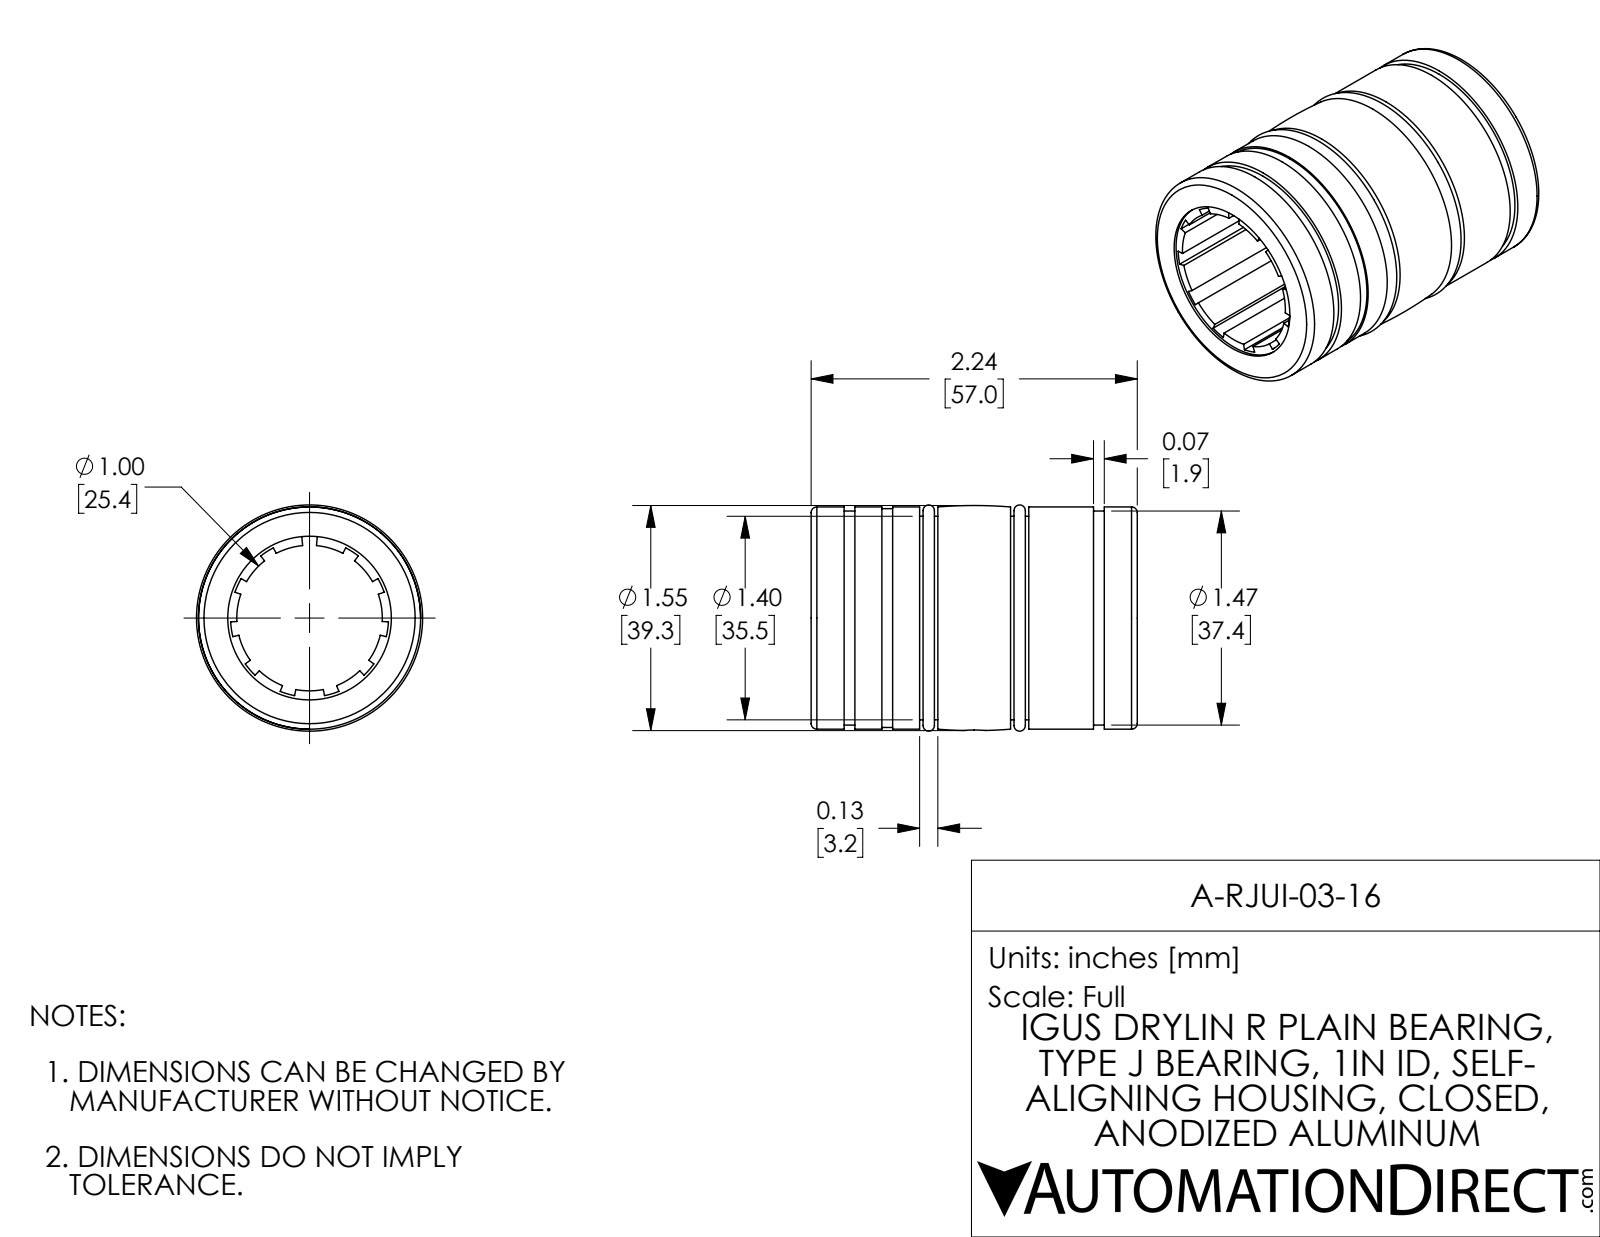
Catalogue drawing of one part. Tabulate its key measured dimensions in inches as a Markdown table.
| quantity | value |
| --- | --- |
| part name | A-RJUI-03-16 |
| STEP written by | SolidWorks 2017 (AUTOMOTIVE_DESIGN) |
| units | inches |
| bodies | 4 solids, 161 faces (81 planar, 66 cylindrical, 14 other) |
| overall size | 2.242 × 1.555 × 1.555 |
| volume | 2.178 in³ |
| surface area | 41.82 in² |
| round holes (diameter × count) | 0.156 × 1, 1.125 × 1, 1.203 × 1 |
| round bosses / shafts (diameter × count) | 1.527 × 1, 1.504 × 1, 1.471 × 1, 1.399 × 1, 1.125 × 1, 0.15 × 1 |
| partial cylindrical surfaces (radius × count) | 0.5 × 1, 0.543 × 1, 0.594 × 1 |
| main face-to-face distances | 2.242, 0.746, 1.496, 0.871, 1.371, 0.125, 0.625, 1.027, 1.215, 0.281 |
